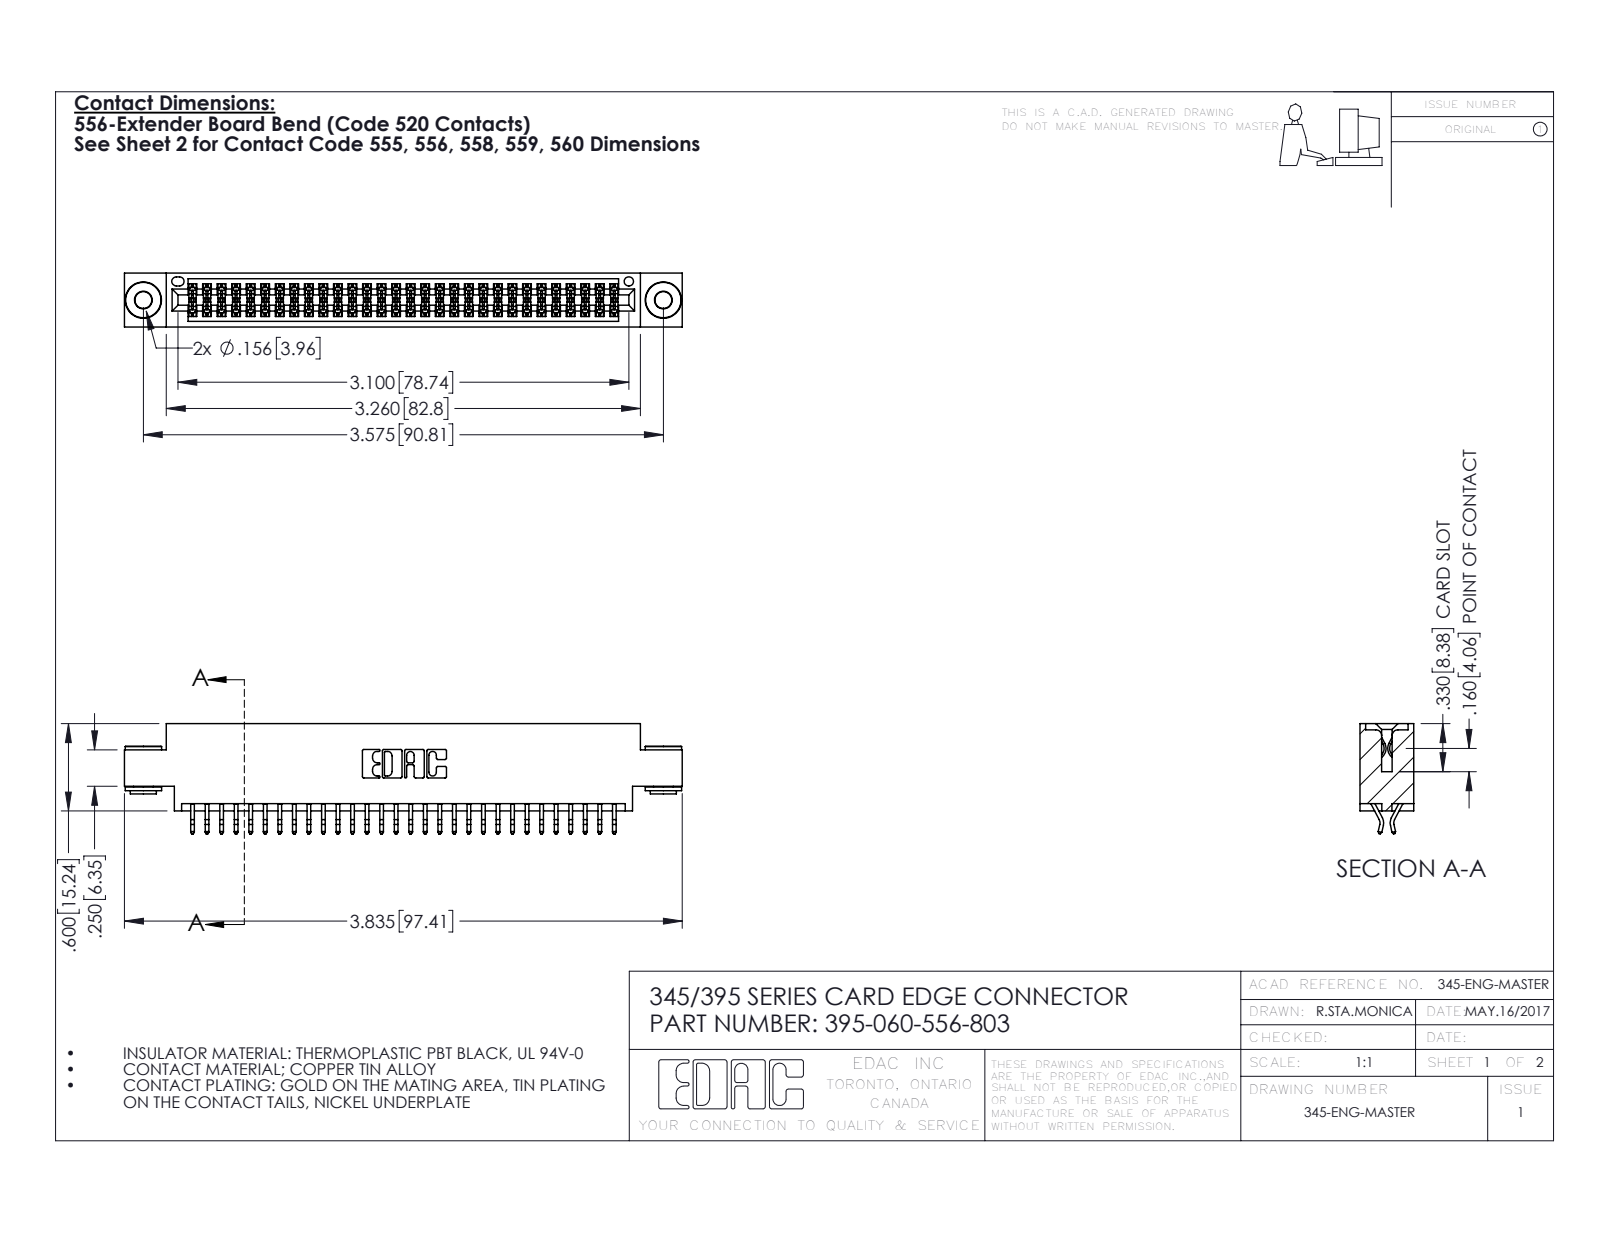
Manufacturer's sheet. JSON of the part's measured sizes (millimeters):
{"part_name": "345-292-001_556 Tail; 345-250-002_345-250-002-102; 345 Part_0.170 Offset - 0.156 Dia-TH; 395-060-556-803", "step_written_by": "SolidWorks 2016 (CONFIG_CONTROL_DESIGN)", "units": "millimeters", "bodies": {"solids": 63, "faces": 3528, "planar": 2314, "cylindrical": 1206, "other": 8}, "overall_size": [97.4, 19.2, 9.4], "volume_mm3": 9260, "surface_area_mm2": 13740, "round_holes": [[2.9, 2], [4, 2], [1.6, 1]], "round_bosses_or_shafts": [[6.4, 2], [4.6, 2], [3.5, 2]], "partial_cylinders_radius": [[0.2, 90], [0.3, 22], [0.2, 6], [0.8, 6], [0.7, 3], [0.3, 2], [0.4, 2], [0.5, 2]], "face_to_face_distances": [1.8, 7.6, 9.4, 5.1, 0.6, 2.5, 6.9, 5.7, 4.4, 3.8], "hole_center_spacings": [6.9, 84.8, 90.8]}
